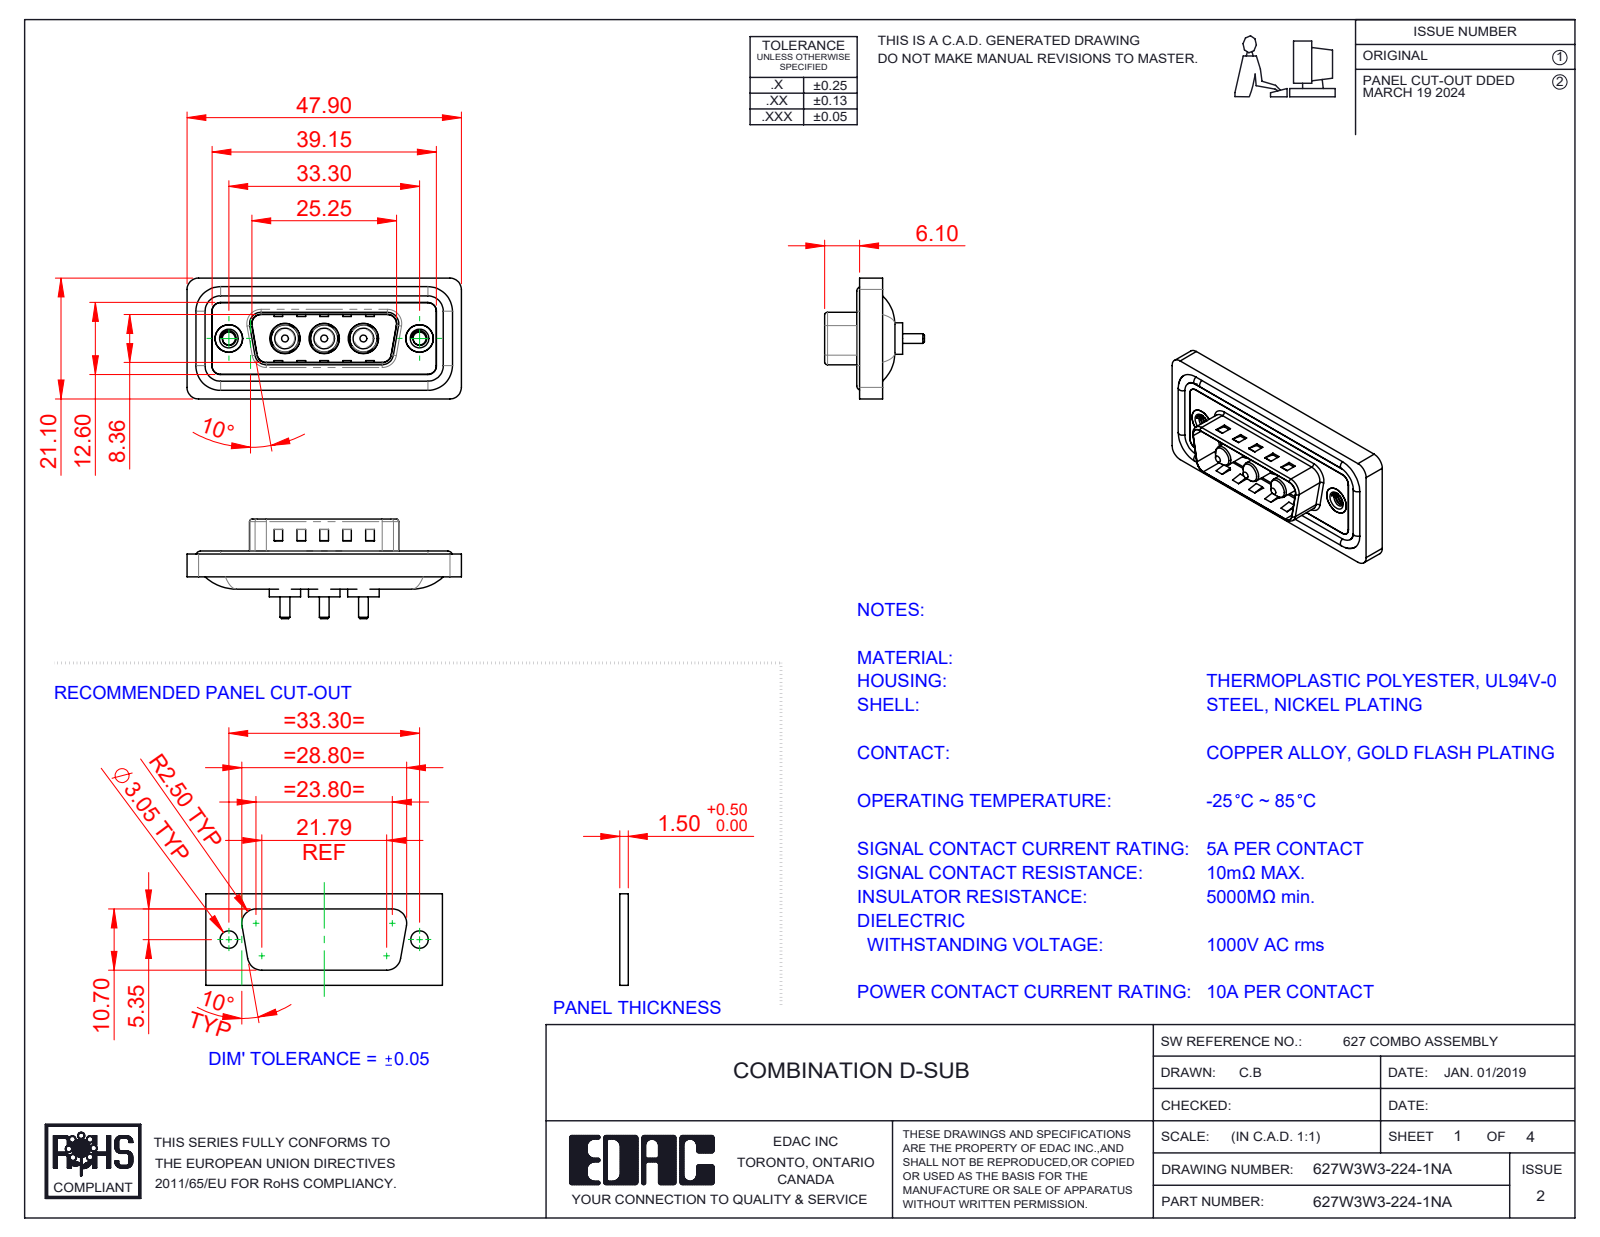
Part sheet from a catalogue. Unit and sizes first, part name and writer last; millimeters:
Units: millimetres
Overall size (bounding box): 47.9 × 21.1 × 17.4
Round holes (diameter × count): ⌀4.85 ×3, ⌀5.3 ×3, ⌀2.26 ×2, ⌀4 ×2, ⌀4.8 ×2, ⌀5 ×2
Round bosses / shafts (diameter × count): ⌀1.6 ×4, ⌀5.5 ×3, ⌀5.2 ×3, ⌀4.75 ×3, ⌀3.75 ×3, ⌀3.6 ×3, ⌀1.7 ×3, ⌀4.9 ×2
Partial cylindrical surfaces — rounded edges, fillets, slot ends (radius × count): R1.5 ×26, R2 ×20, R0.5 ×8, R1.6 ×8, R0.25 ×4, R0.6 ×4, R0.65 ×4, R0.9 ×4
Main face-to-face distances: 0.4, 1.5, 1.1, 0.5, 1.6, 3.1, 2.9, 4, 0.82, 9.58
Hole centre spacings: 6.85, 9.8, 16.65, 23.5, 13.7, 33.3
Volume: 5 543 mm³ · Surface area: 8 713 mm²
Bodies: 13 solids, 562 faces (207 planar, 243 cylindrical, 112 other)
Part name (STEP PRODUCT): 627W3W3-224-1NA; 627Combo Threaded Rivet_A; 627Combo Waterproof Housing_15 Contacts; Power Pin_10A S (+3 more)
STEP written by: SolidWorks 2023 (CONFIG_CONTROL_DESIGN)
